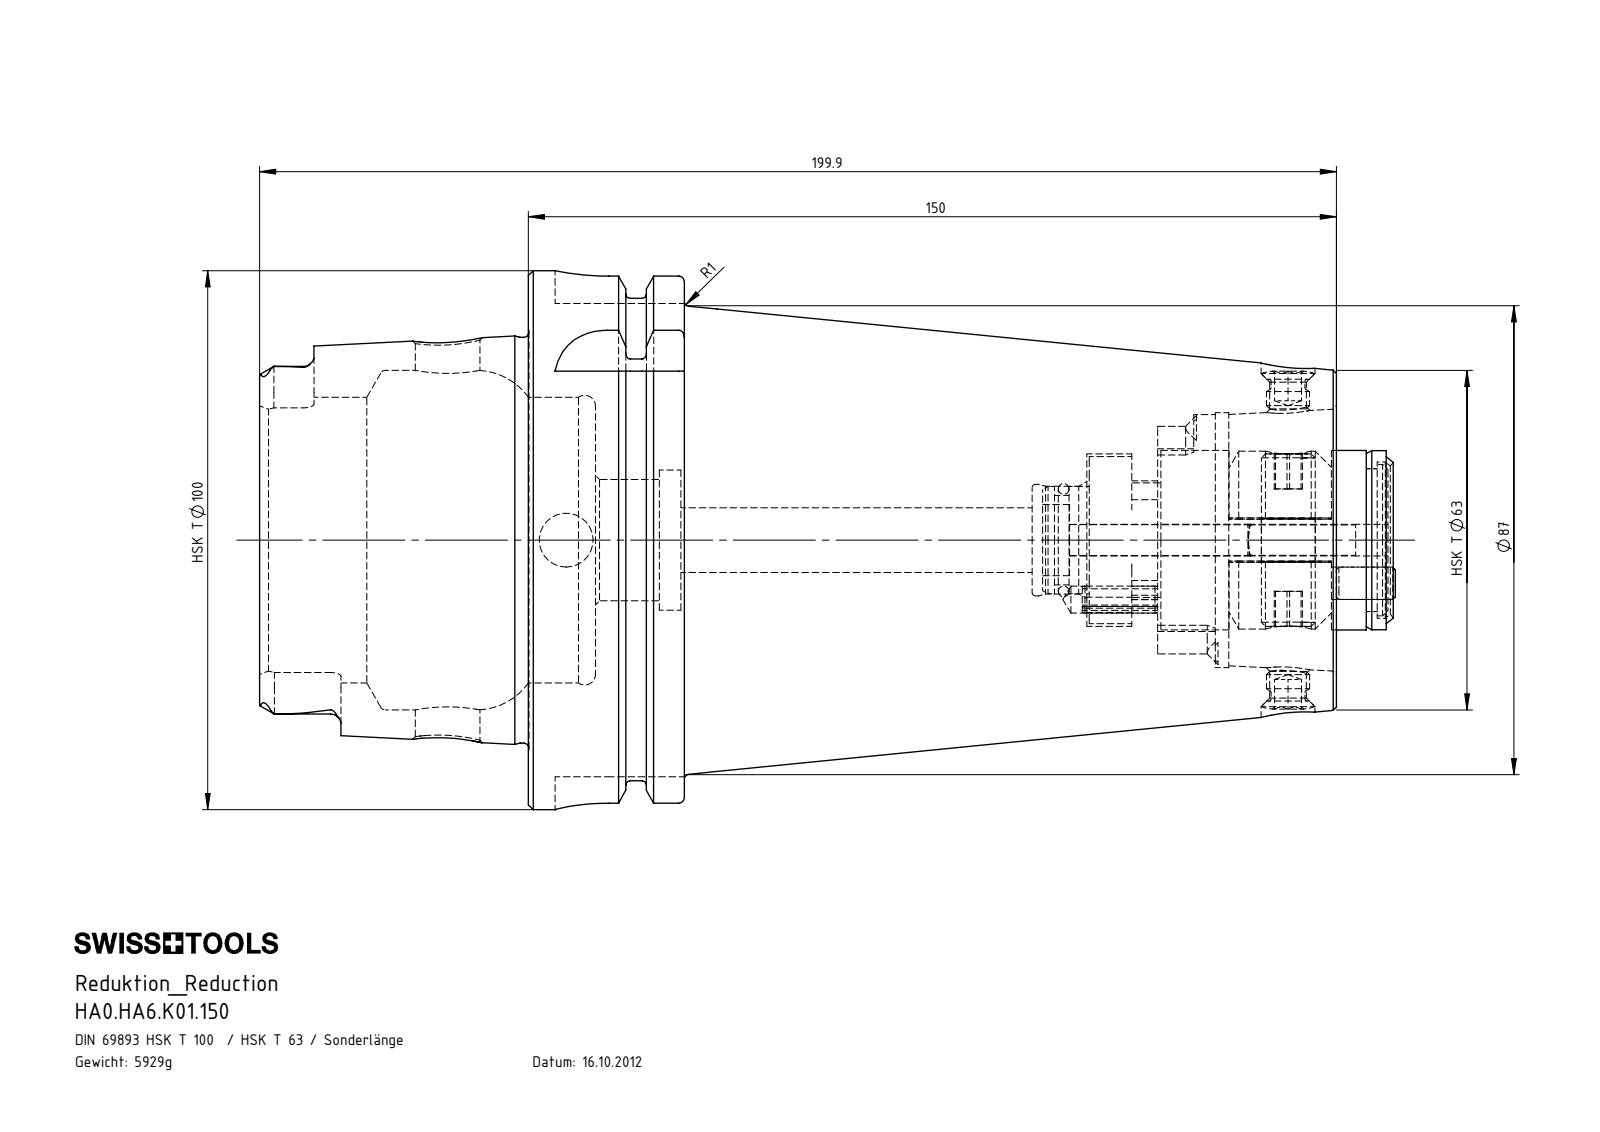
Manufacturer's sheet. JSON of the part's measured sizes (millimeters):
{"part_name": "DIN 3771 - 17x2; Grundkörper1; Stift6; HA0-HA6.K01.150 (+7 more)", "step_written_by": "SolidWorks 2017 (CONFIG_CONTROL_DESIGN)", "units": "millimeters", "bodies": {"solids": 11, "faces": 350, "planar": 158, "cylindrical": 97, "other": 95}, "overall_size": [210.85, 100, 100], "volume_mm3": 755451, "surface_area_mm2": 105644, "round_holes": [[10, 3], [5.75, 2], [5.8, 2], [12, 2], [4, 1], [5, 1], [6, 1], [6.8, 1], [8.5, 1], [13.2, 1], [20, 1], [20.7, 1]], "round_bosses_or_shafts": [[100, 1], [91.95, 1], [75.26, 1], [33.3, 1], [33.25, 1], [33, 1], [28.1, 1], [21.25, 1]], "partial_cylinders_radius": [[3, 12], [1.9, 6], [2.9, 4], [4.88, 4], [10, 4], [1, 2], [2.88, 2], [4.05, 1]], "face_to_face_distances": [12.45, 16.5, 28.95, 8, 19.95, 150, 137.55, 121.05, 116.8, 104.35], "hole_center_spacings": [8, 11.31, 9.94, 11.2, 14.58, 16, 20.68, 156]}
